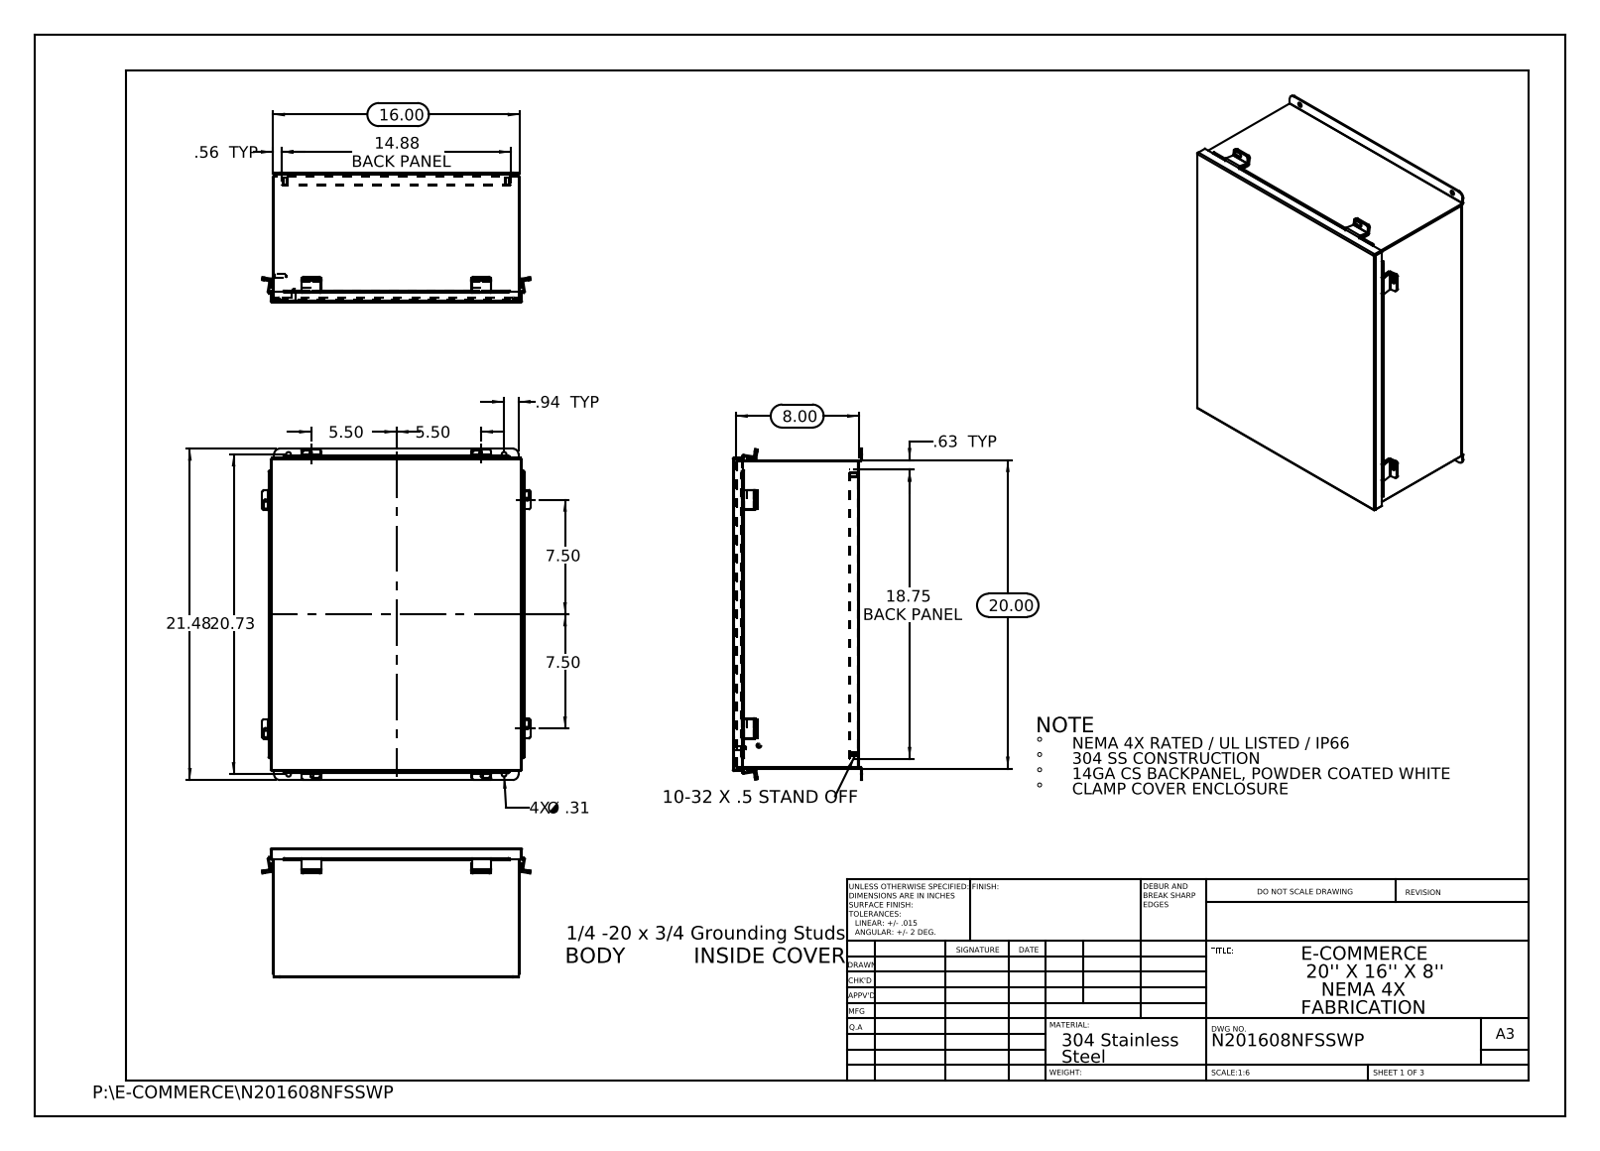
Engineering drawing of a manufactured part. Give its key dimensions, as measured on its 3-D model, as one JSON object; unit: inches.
{"part_name": "N201608NFSSWP JIC_Standoff; N201608NFSSWP JIC Cover Clamp; N201608NFSSWP JIC Bottom; N201608NFSSWP JIC Backpanel (+6 more)", "step_written_by": "SolidWorks 2013 (CONFIG_CONTROL_DESIGN)", "units": "inches", "bodies": {"solids": 27, "faces": 640, "planar": 420, "cylindrical": 200, "other": 20}, "overall_size": [21.476, 17.407, 8.39], "volume_in3": 121.6, "surface_area_in2": 3282, "round_holes": [[0.25, 12], [0.187, 4], [0.312, 4]], "round_bosses_or_shafts": [[0.313, 4], [0.315, 2], [0.236, 2]], "partial_cylinders_radius": [[0.125, 32], [0.009, 16], [0.133, 16], [0.013, 12], [0.088, 12], [0.083, 8], [0.1, 8], [0.084, 4]], "face_to_face_distances": [0.075, 8.128, 8.053, 8.203, 15.925, 7.628, 0.575, 0.5, 7.553, 0.649], "hole_center_spacings": [1.315, 14.235, 19.427, 24.048, 11, 13.976, 14.375, 14.85]}
